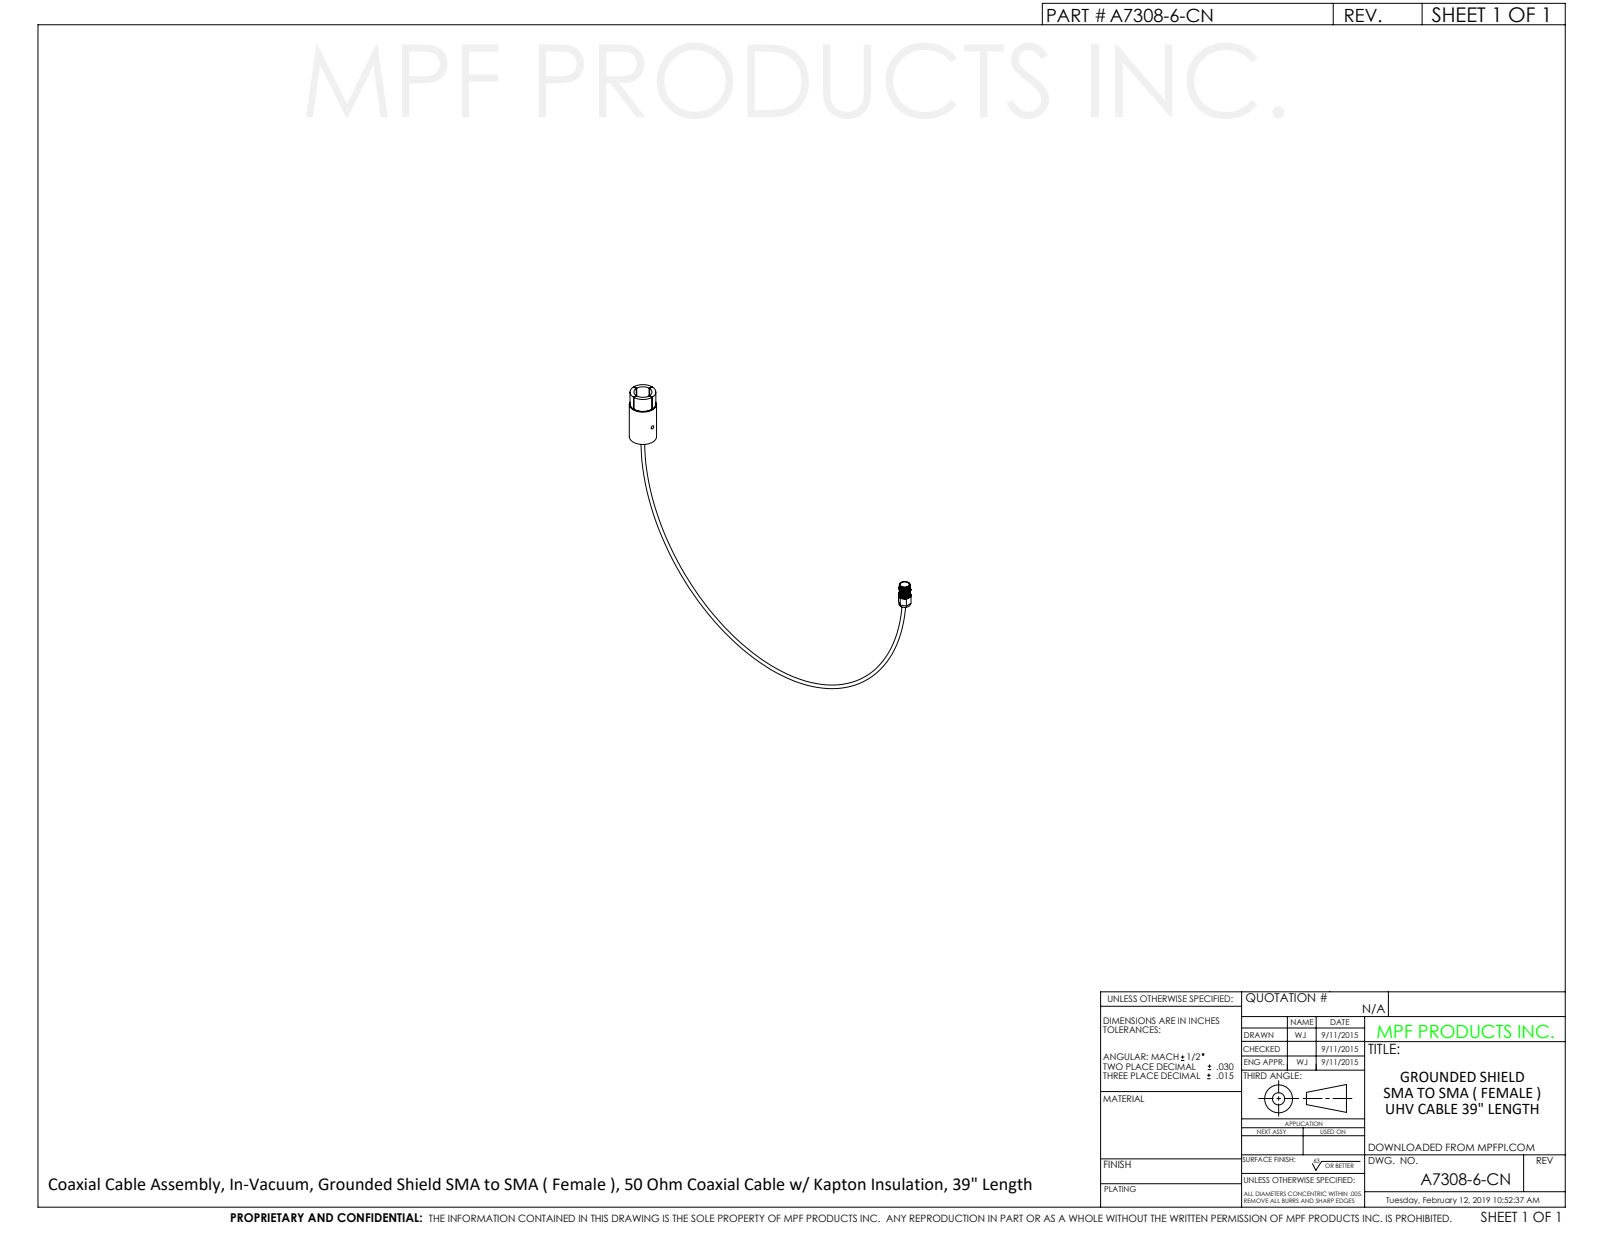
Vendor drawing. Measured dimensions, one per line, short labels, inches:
name: A7300 FEMALE SMA PART; A7307-6-CN; A7301-3_JUST CABLE
written by: SolidWorks 2012 (CONFIG_CONTROL_DESIGN)
unit: in
bodies: 4 solids, 200 faces (71 planar, 48 cylindrical, 81 other)
size: 10.654 × 6.833 × 0.75
volume: 0.53 in³; area: 13.7 in²
holes: 2× ⌀0.1, 1× ⌀0.05, 1× ⌀0.167, 1× ⌀0.186, 1× ⌀0.251, 1× ⌀0.257, 1× ⌀0.293, 1× ⌀0.5
bosses: 1× ⌀0.75, 1× ⌀0.71, 1× ⌀0.307, 1× ⌀0.294, 1× ⌀0.25, 1× ⌀0.207, 1× ⌀0.18, 1× ⌀0.165
face distances: 1.5, 0.2, 1.3, 0.02, 0.308, 0.328, 0.623, 0.823, 2.123, 0.308
hole spacings: 10.12, 10.121
